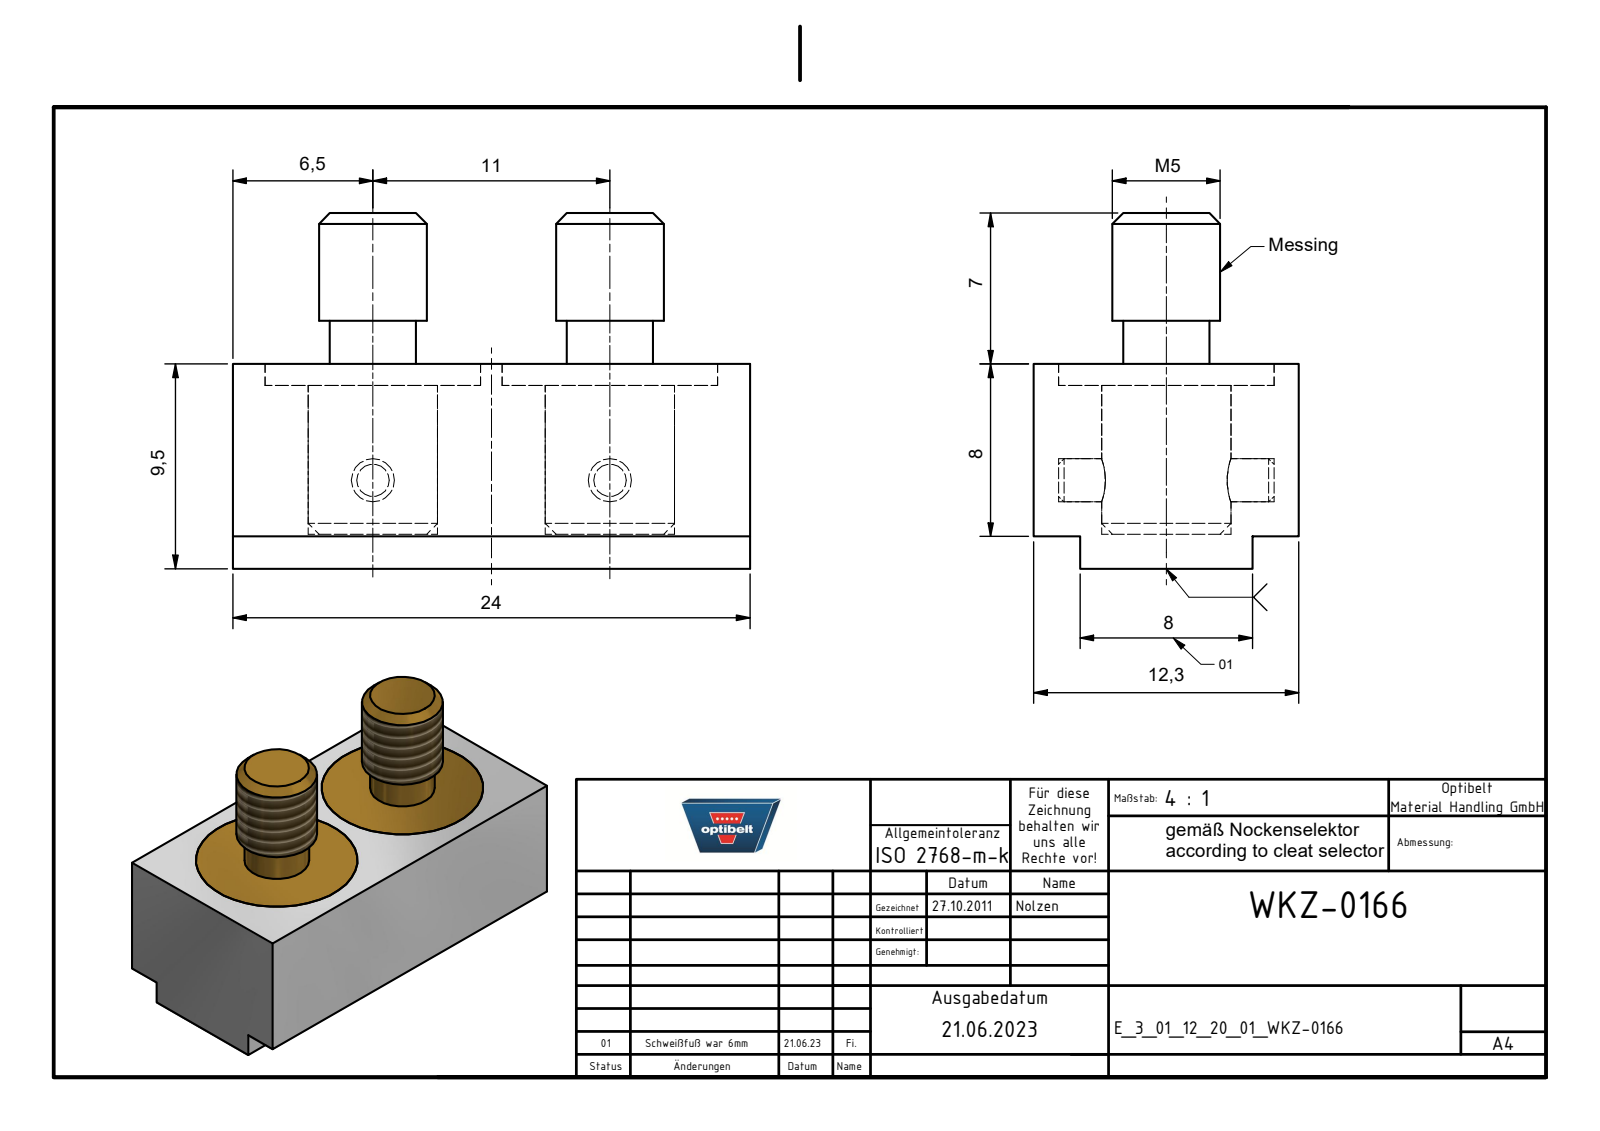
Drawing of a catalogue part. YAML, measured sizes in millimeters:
part_name: "E_3_01_12_20_01_WKZ-0166; E_3_01_12_20_01_WKZ-0166-Teil1; E_3_01_12_20_01_WKZ-0166-Teil2"
step_written_by: "Autodesk Inventor 2021 (AUTOMOTIVE_DESIGN)"
units: millimeters
bodies: {solids: 3, faces: 60, planar: 32, cylindrical: 20, other: 8}
overall_size: [24, 16.5, 12.3]
volume: 2887
surface_area: 2542
round_holes:
  - {diameter: 2, count: 2}
  - {diameter: 6, count: 2}
  - {diameter: 10, count: 2}
round_bosses_or_shafts:
  - {diameter: 5, count: 2}
  - {diameter: 4, count: 2}
face_to_face_distances: [1, 12.3, 8.5, 9.5, 8, 7, 24, 1.5, 1.6, 6.9]
hole_center_spacings: [11]
